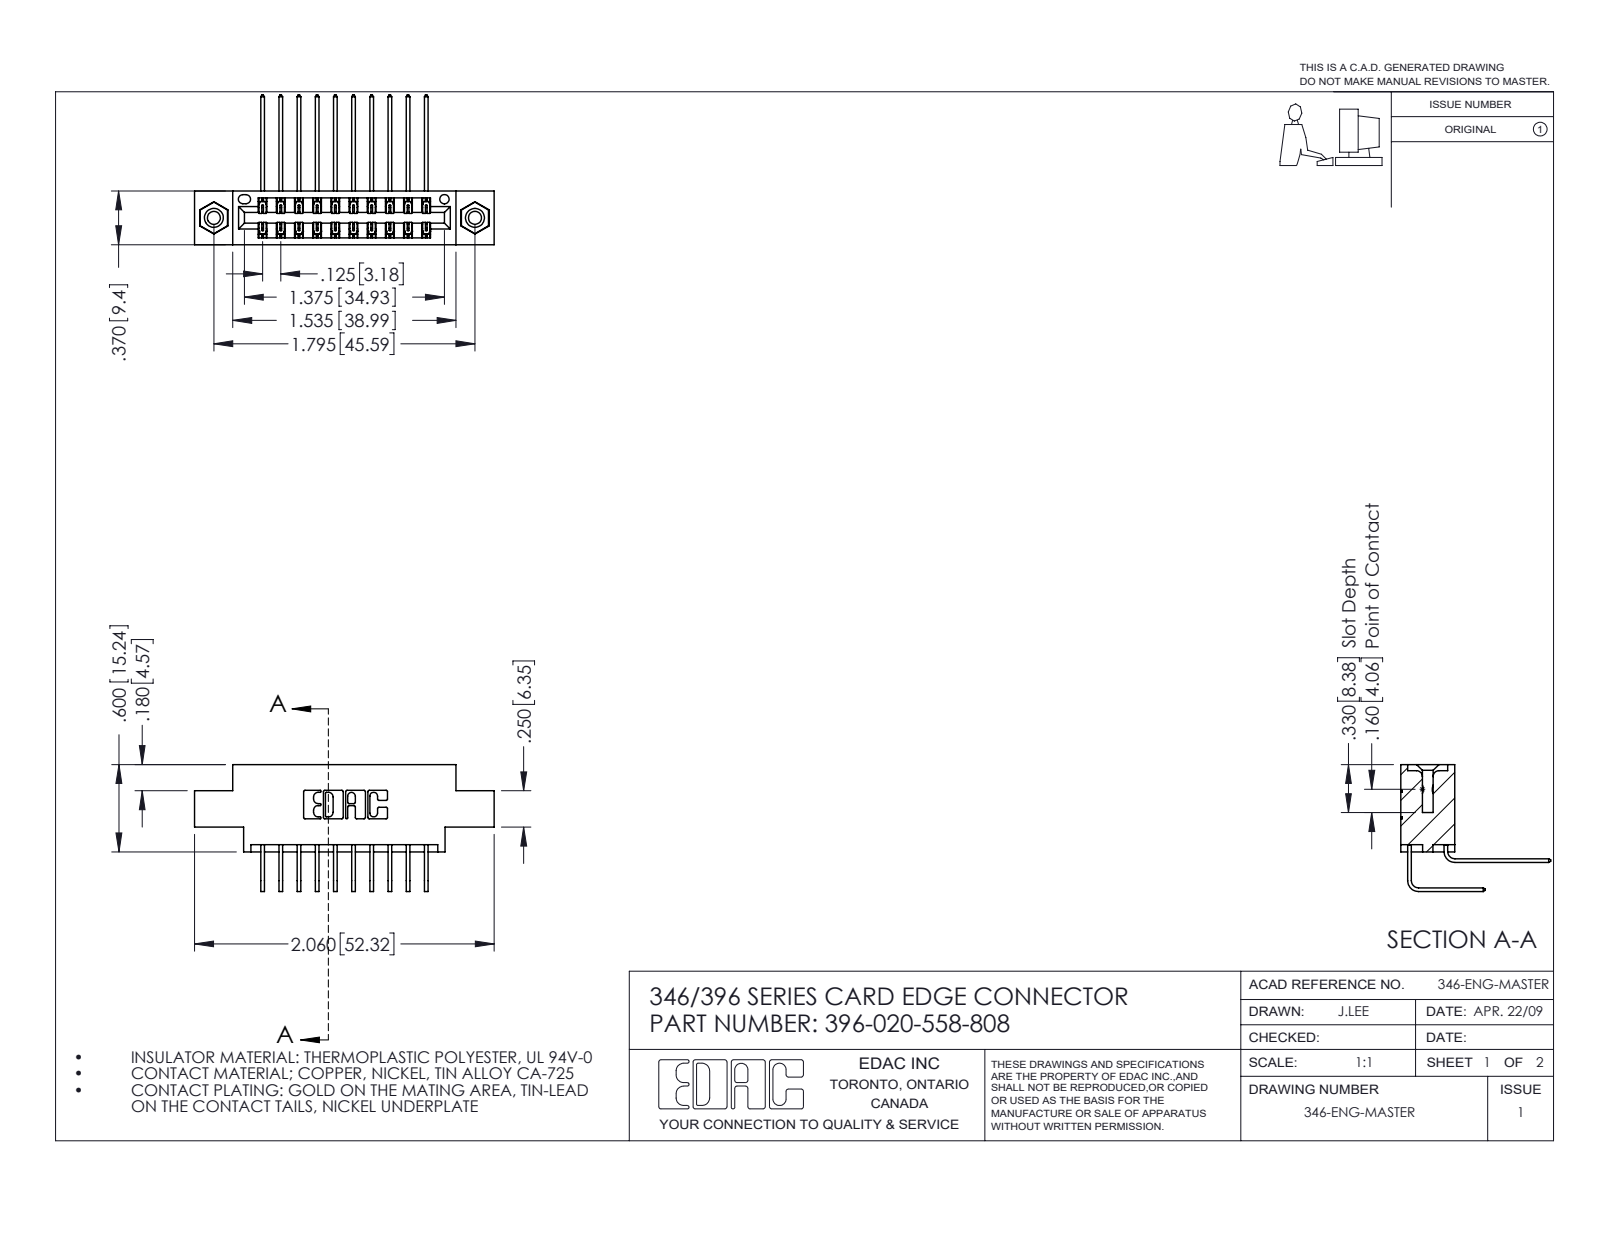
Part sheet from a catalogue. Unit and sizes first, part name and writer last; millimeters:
Units: millimetres
Overall size (bounding box): 52.3 × 26.2 × 22.2
Round holes (diameter × count): ⌀2.3 ×2, ⌀3.2 ×2, ⌀4 ×2, ⌀1.6 ×1
Round bosses / shafts (diameter × count): ⌀3.9 ×2
Partial cylindrical surfaces — rounded edges, fillets, slot ends (radius × count): R0.2 ×30, R0.3 ×22, R0.2 ×6, R0.8 ×6, R0.7 ×3, R0.4 ×2, R0.6 ×2, R0.6 ×2
Main face-to-face distances: 6.4, 1.2, 8.2, 9.4, 0.6, 1.8, 7.6, 5.6, 3.8, 7
Hole centre spacings: 6.2, 40.4, 45.6
Volume: 4 800 mm³ · Surface area: 6 858 mm²
Bodies: 23 solids, 1266 faces (852 planar, 398 cylindrical, 16 other)
Part name (STEP PRODUCT): 345-292-001_558 559 Tail - 1; 346 Part_0.170 Offset - 0.156 Dia-TI; 345-292-001_558 Tail - 2; 396-020-558-808 (+1 more)
STEP written by: SolidWorks 2016 (CONFIG_CONTROL_DESIGN)
